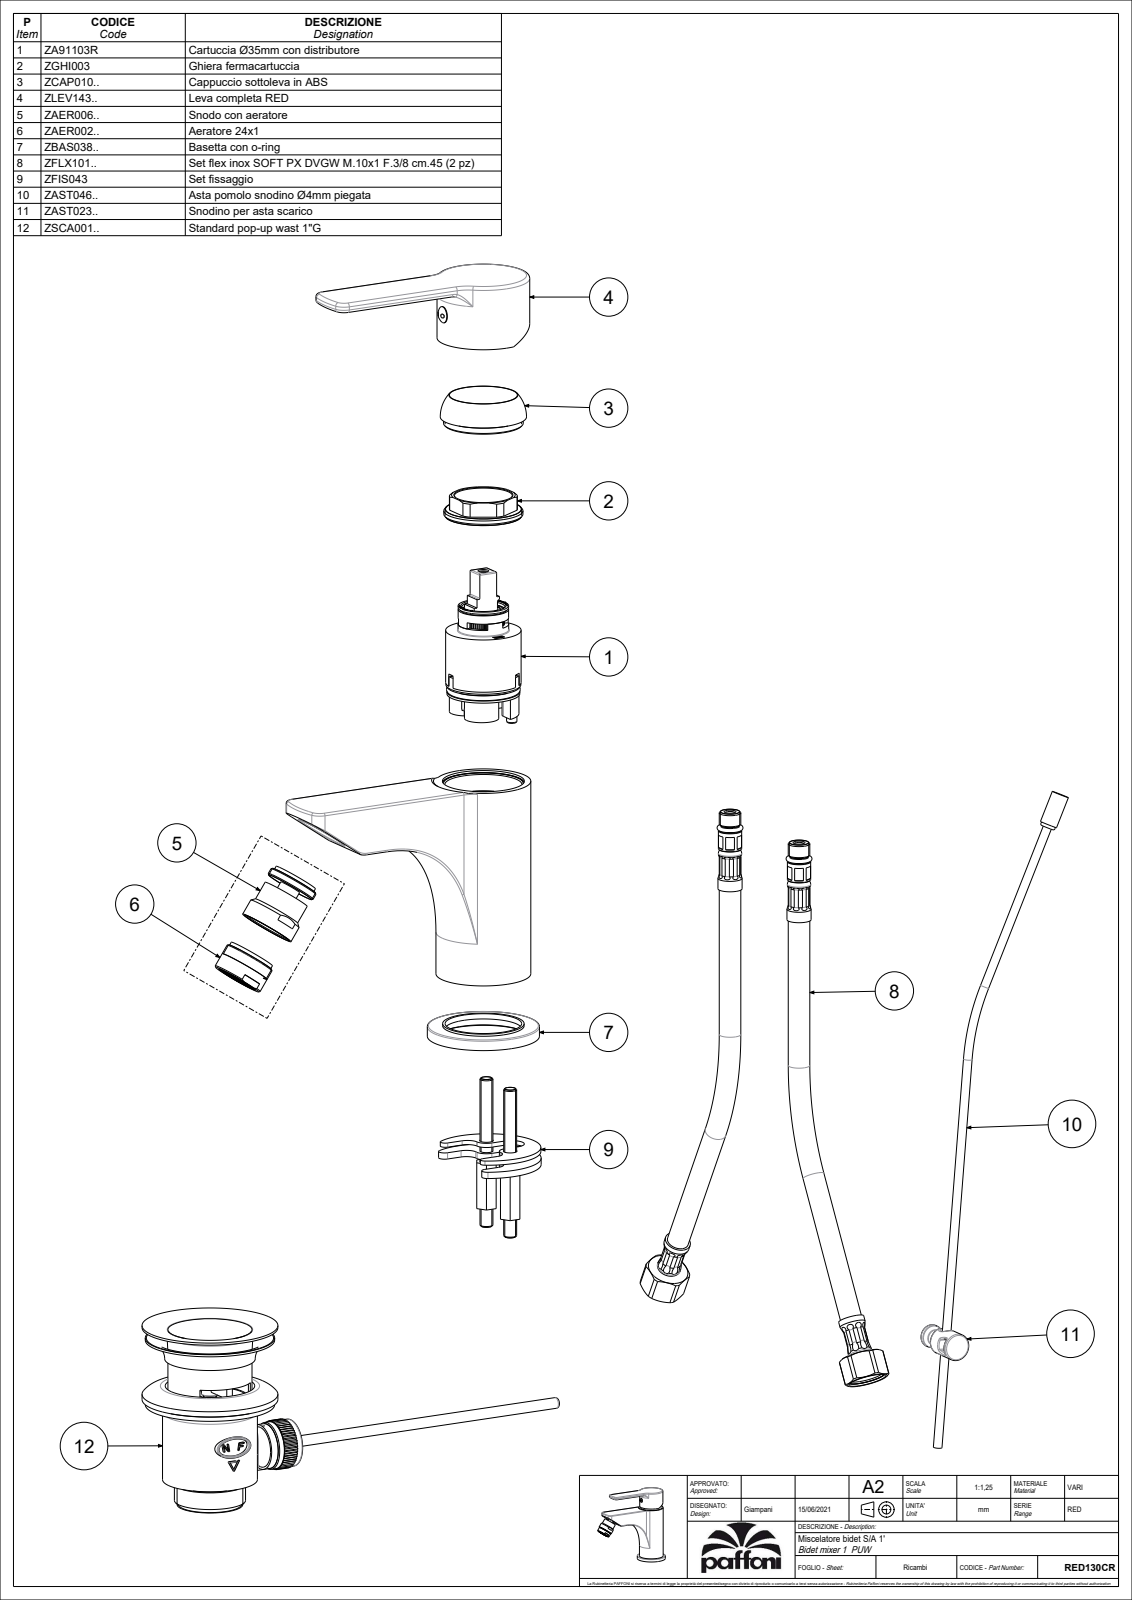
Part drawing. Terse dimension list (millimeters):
name: RED135CR
written by: CREO PARAMETRIC BY PTC INC, 2020044 (CONFIG_CONTROL_DESIGN)
unit: mm
bodies: 6 solids, 3098 faces (2178 planar, 536 cylindrical, 384 other)
size: 152.43 × 130.73 × 52
volume: 147 760 mm³; area: 96 792 mm²
holes: 4× ⌀5, 3× ⌀4.5, 3× ⌀8, 3× ⌀9, 3× ⌀12, 2× ⌀3.3, 2× ⌀4, 2× ⌀6, 2× ⌀6.5, 2× ⌀11, 2× ⌀16, 1× ⌀3
bosses: 3× ⌀10, 2× ⌀11.2, 2× ⌀10.8, 2× ⌀6, 2× ⌀4.8, 1× ⌀52, 1× ⌀44, 1× ⌀43
rounds: 100× R0.5, 14× R1.26, 14× R2.05, 11× R0.15, 10× R1, 9× R0.3, 6× R5, 5× R10
face distances: 3.5, 27.5, 28, 31, 4.5, 31.5, 3, 36, 32.5, 24
hole spacings: 0.71, 8.51, 8.6, 9.66, 9.85, 13.04, 13.21, 13.45
